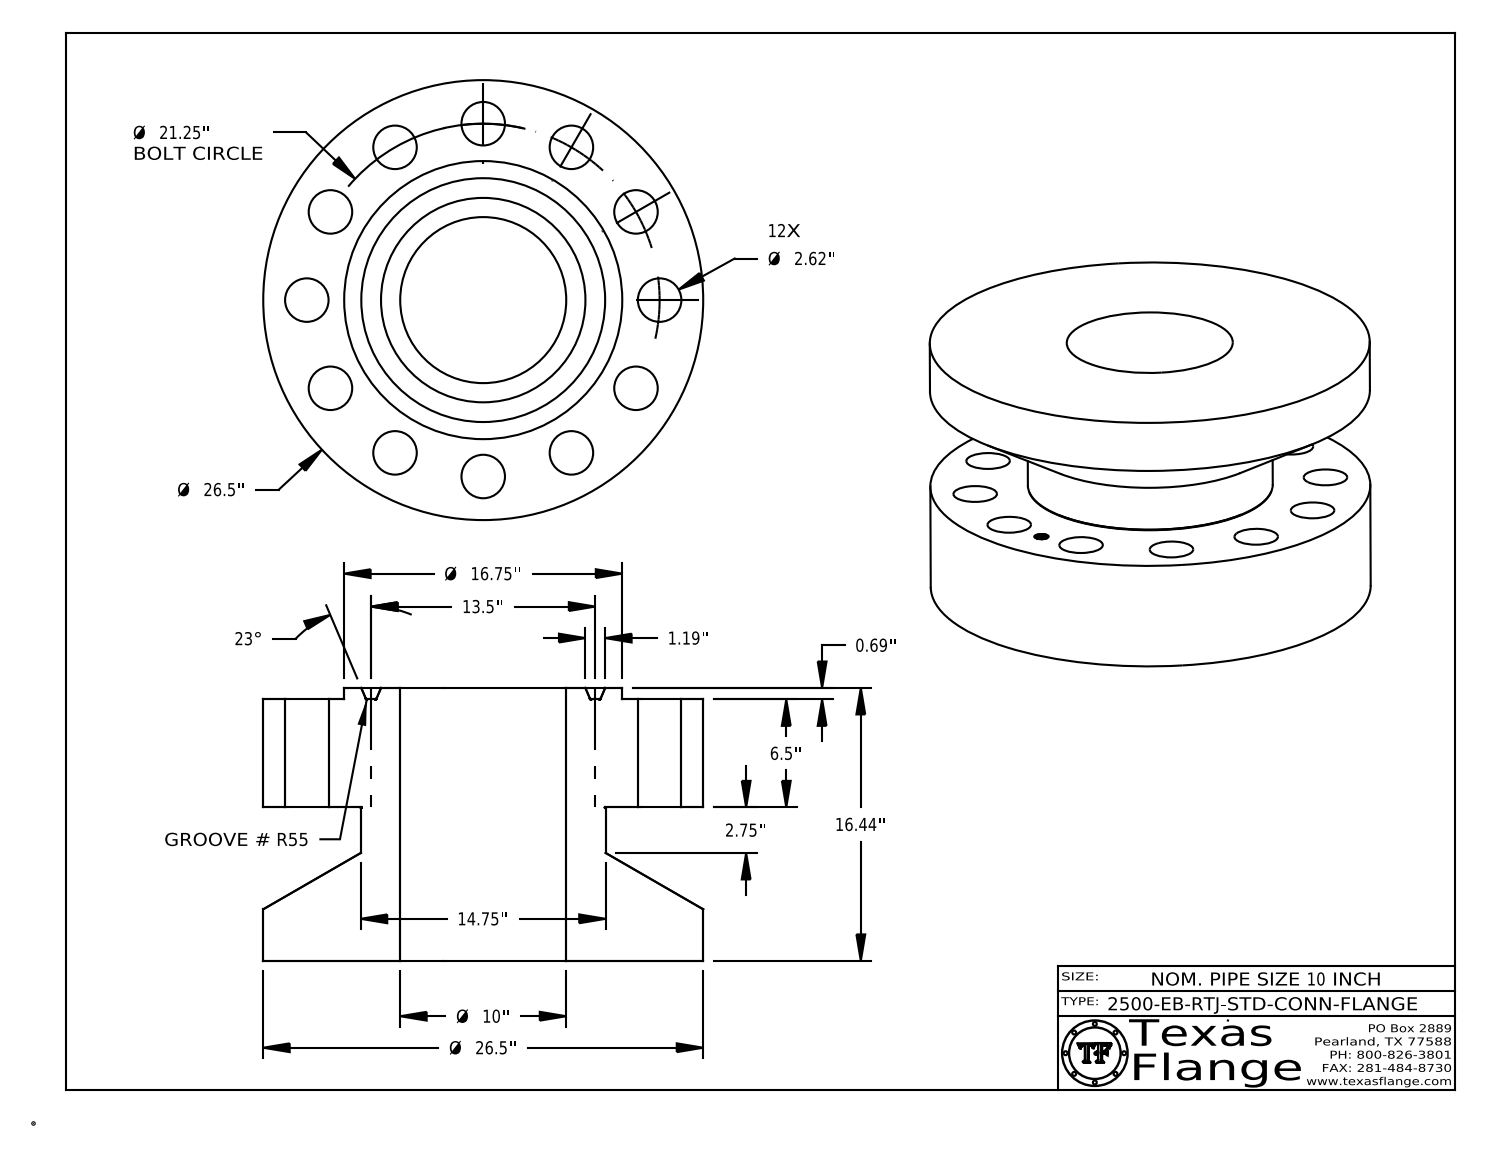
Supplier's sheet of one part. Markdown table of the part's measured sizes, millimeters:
| quantity | value |
| --- | --- |
| part name | 10-2500-EB-RTJ-STD-CONN-FLANGE |
| STEP written by | CATIA V5 STEP AP214 (AUTOMOTIVE_DESIGN) |
| units | millimeters |
| bodies | 1 solid, 439 faces (371 planar, 54 cylindrical, 14 other) |
| overall size | 673.1 × 673.1 × 417.5 |
| volume | 87 620 000 mm³ |
| surface area | 2 450 000 mm² |
| round holes (diameter × count) | 66.5 × 12, 21.6 × 1, 254 × 1 |
| round bosses / shafts (diameter × count) | 1.3 × 8, 673.1 × 1, 425.5 × 1, 374.7 × 1, 17 × 1 |
| main face-to-face distances | 235, 165.1, 400.1, 17.5, 182.6, 417.5, 182.4, 165, 235.1, 6.5 |
| hole center spacings | 269.9, 139.7, 467.4, 381.7, 521.4, 381.7, 521.4, 539.8 |
